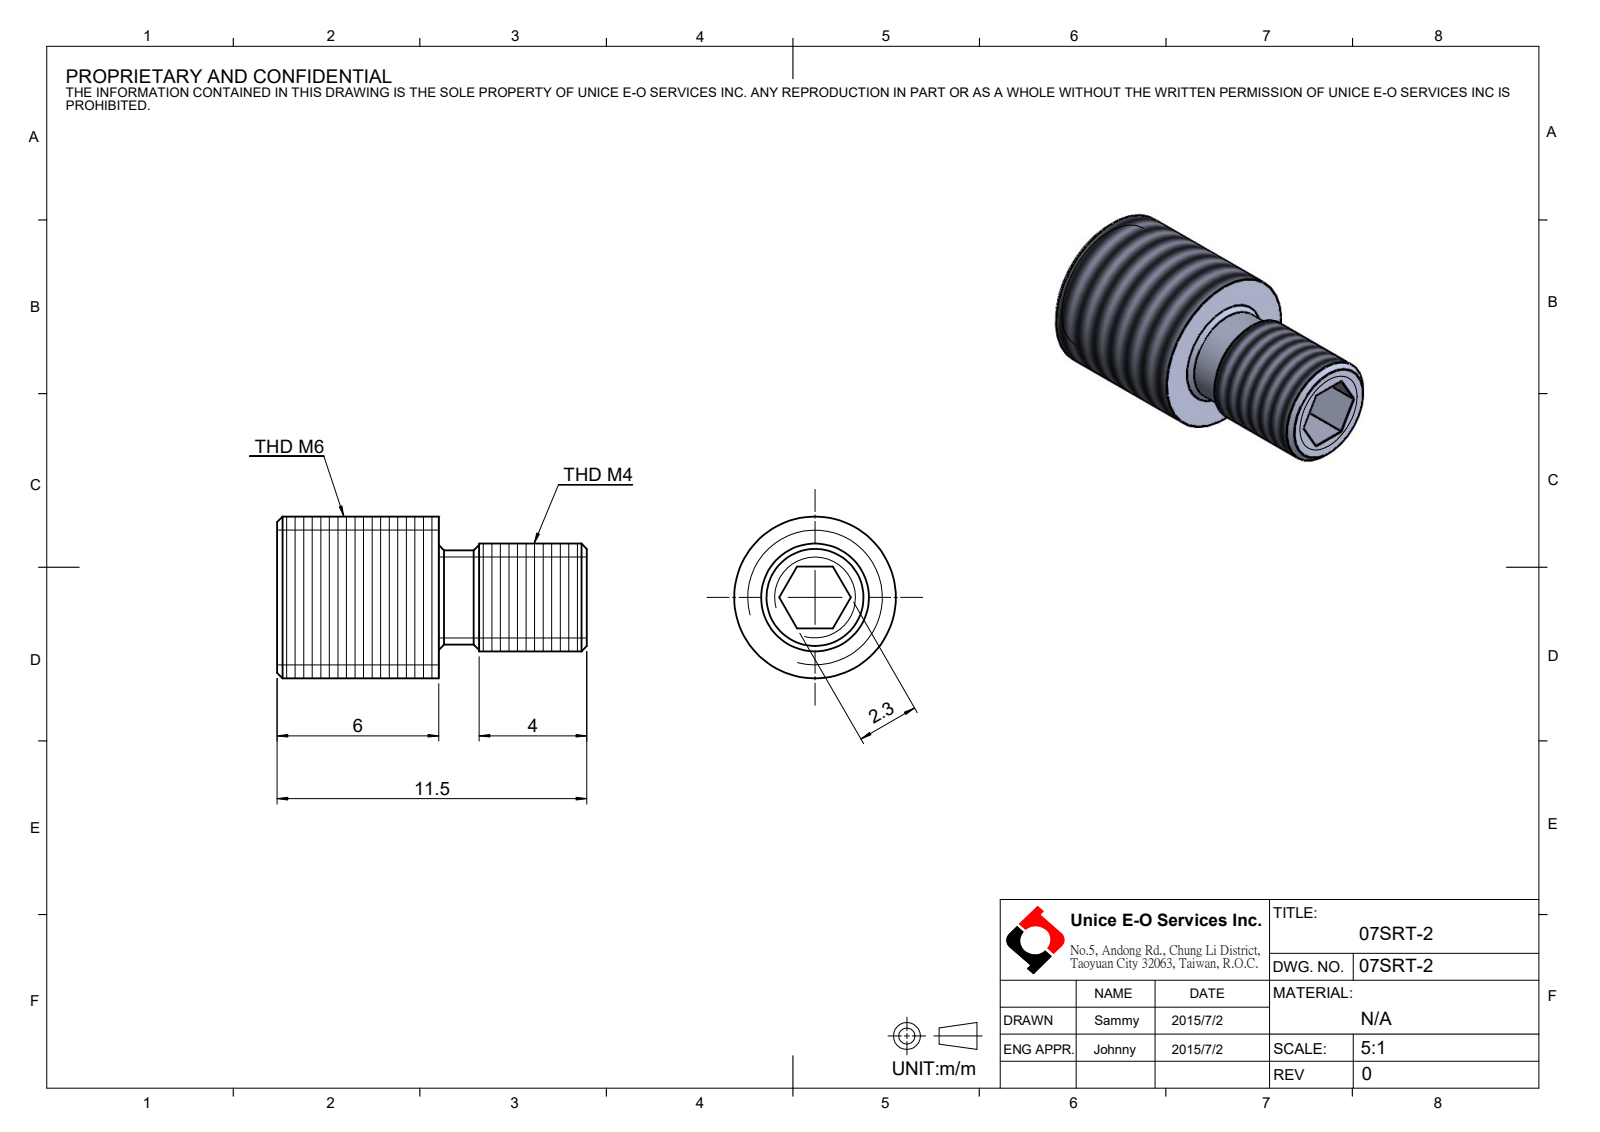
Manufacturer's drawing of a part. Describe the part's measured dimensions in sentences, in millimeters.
The part is named "07SRT-2". Its 3-D file was written by "SolidWorks 2016 (CONFIG_CONTROL_DESIGN)". It is 1 solid with 32 faces: 18 planar, 6 cylindrical and 8 other. Overall it measures 11.5 by 6 by 6 millimeters. Its volume is 207 cubic millimeters and its surface area 284 square millimeters. Round bosses or shafts: 1 of diameter 6, 1 of diameter 4, 1 of diameter 3.5. The main face-to-face distances are 2.3, 6, 3, 5.5, 8.5, 11.5, 2.5, 7.5, 4.5, 1.5.
